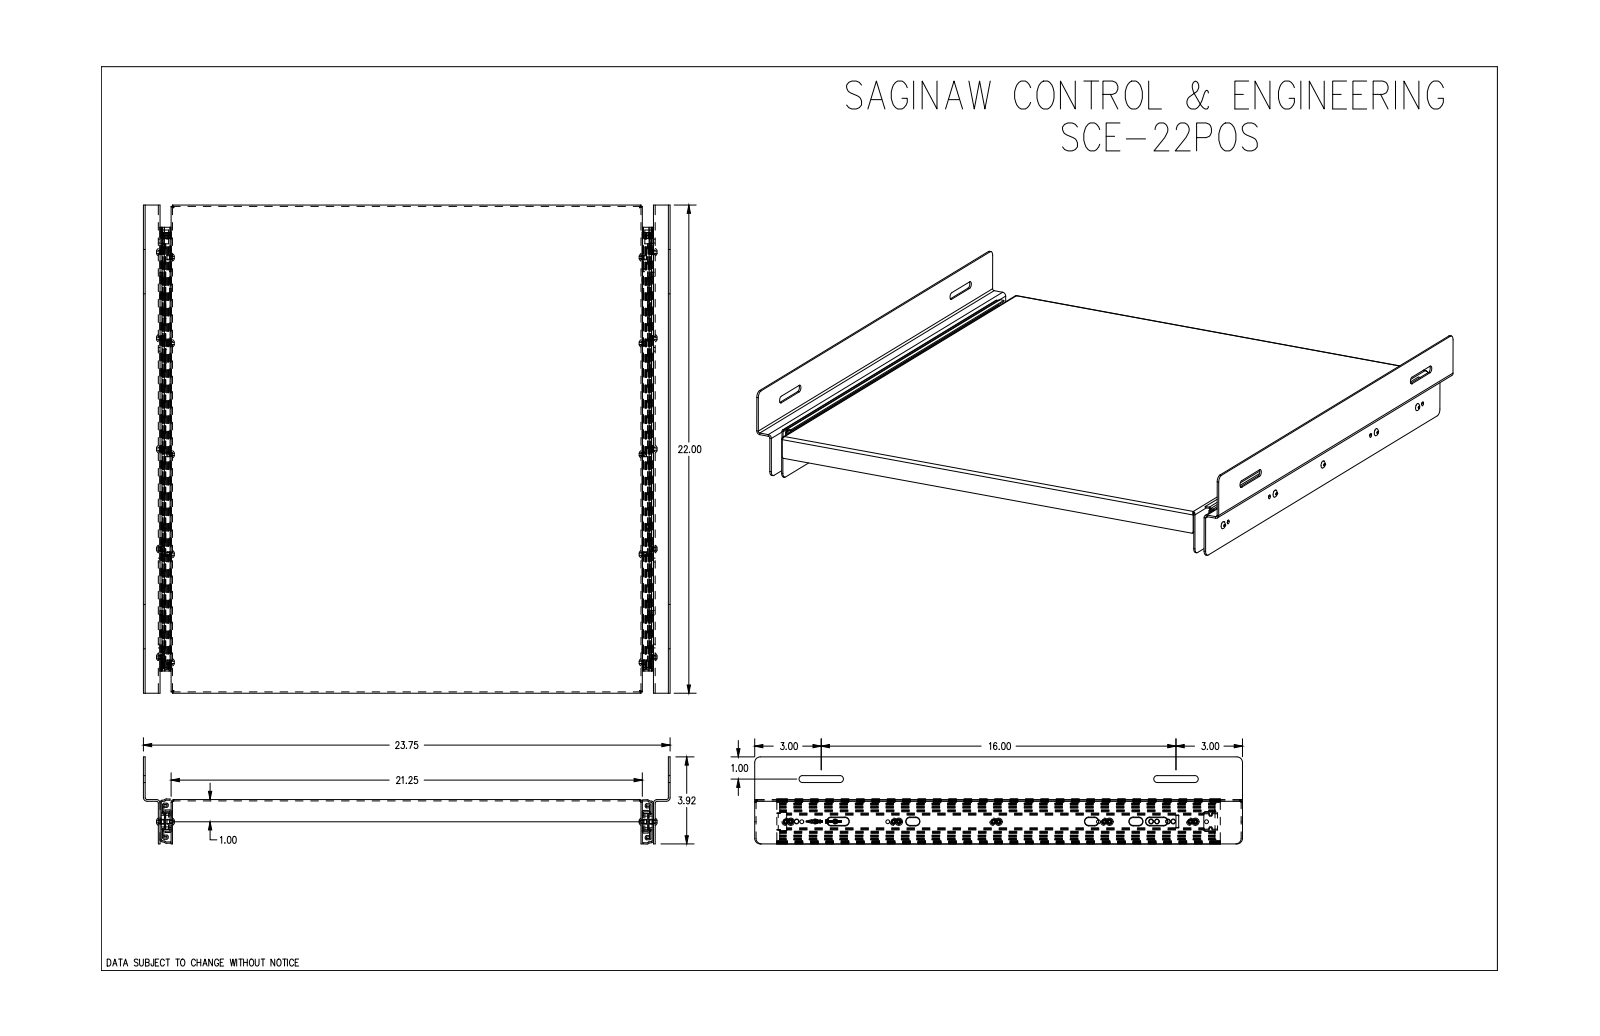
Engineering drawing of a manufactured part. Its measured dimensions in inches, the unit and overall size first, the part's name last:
Units: inches
Overall size (bounding box): 23.753 × 22 × 3.928
Round holes (diameter × count): ⌀0.2 ×34, ⌀0.172 ×18, ⌀0.097 ×10, ⌀0.156 ×10
Round bosses / shafts (diameter × count): ⌀0.216 ×10, ⌀0.16 ×10
Partial cylindrical surfaces — rounded edges, fillets, slot ends (radius × count): R0.032 ×21, R0.188 ×20, R0.062 ×16, R0.02 ×4, R0.034 ×4, R0.04 ×4, R0.041 ×4, R0.05 ×4
Main face-to-face distances: 0.06, 0.078, 0.672, 23.003, 21.19, 22.331, 0.055, 0.75, 23.081, 0.594
Hole centre spacings: 0.5, 0.235, 18.25, 0.235, 16.25, 4.5, 9.5, 1.735
Volume: 65.62 in³ · Surface area: 2 125 in²
Bodies: 29 solids, 690 faces (324 planar, 286 cylindrical, 80 other)
Part name (STEP PRODUCT): SCE-22POS
STEP written by: SolidWorks 2021 (AUTOMOTIVE_DESIGN)
